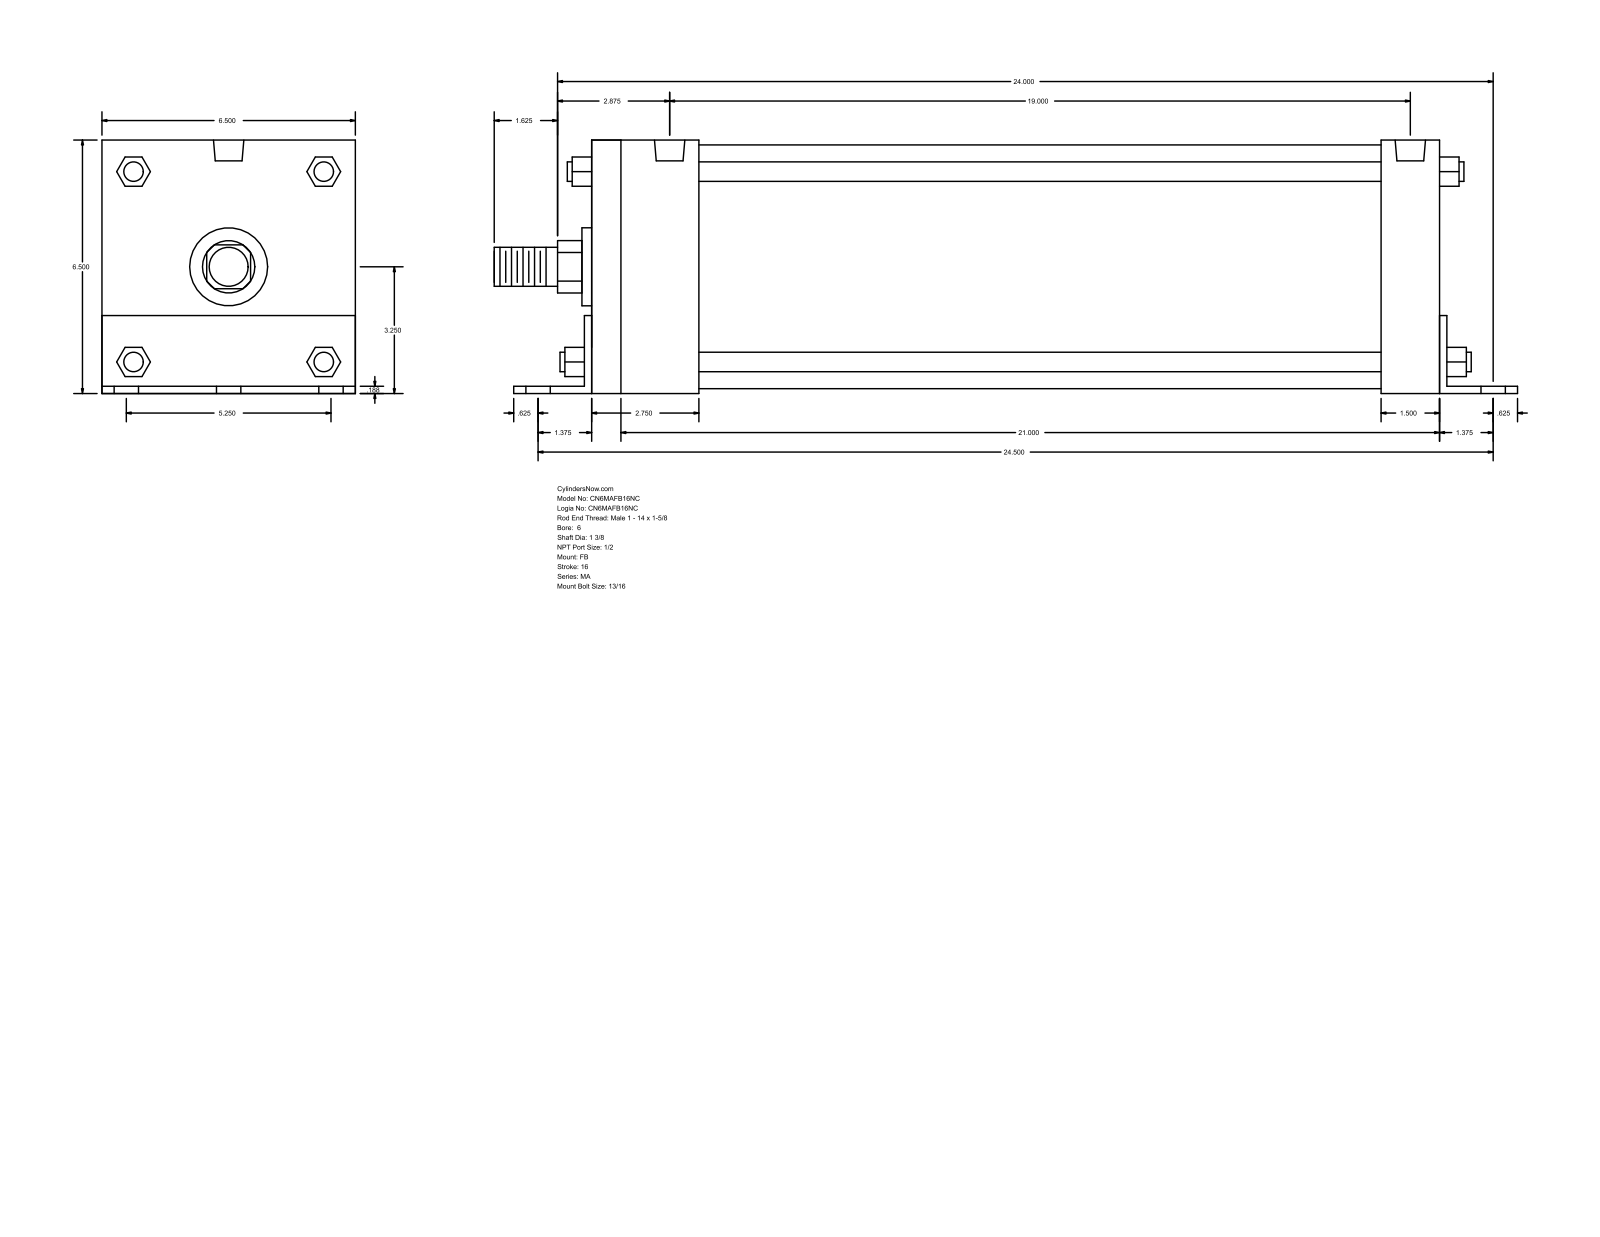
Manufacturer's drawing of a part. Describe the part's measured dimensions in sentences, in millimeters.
The part is named "MA_FB__0600_1.375". Its 3-D file was written by "GSSL Pune (CONFIG_CONTROL_DESIGN)". It is 0 solids with 140 faces: 105 planar, 35 cylindrical and 0 other. Overall it measures 663.58 by 165.15 by 165.1 millimeters. Round holes: 6 of diameter 20.64, 4 of diameter 17.46, 2 of diameter 19.77. Round bosses or shafts: 4 of diameter 12.7, 1 of diameter 158.75, 1 of diameter 50.8, 1 of diameter 34.92, 1 of diameter 25.4. Partial cylindrical surfaces (rounded edges, fillets, slot ends): 1 of radius 17.06, 1 of radius 32.05. The main face-to-face distances are 165.1, 4.76, 549.27, 165.15, 4.71, 160.39, 4.77, 38.1, 42.86, 558.8. The hole center spacings are 66.67, 622.7, 619.12, 83.82, 85.78, 108.6, 133.34, 479.42.
